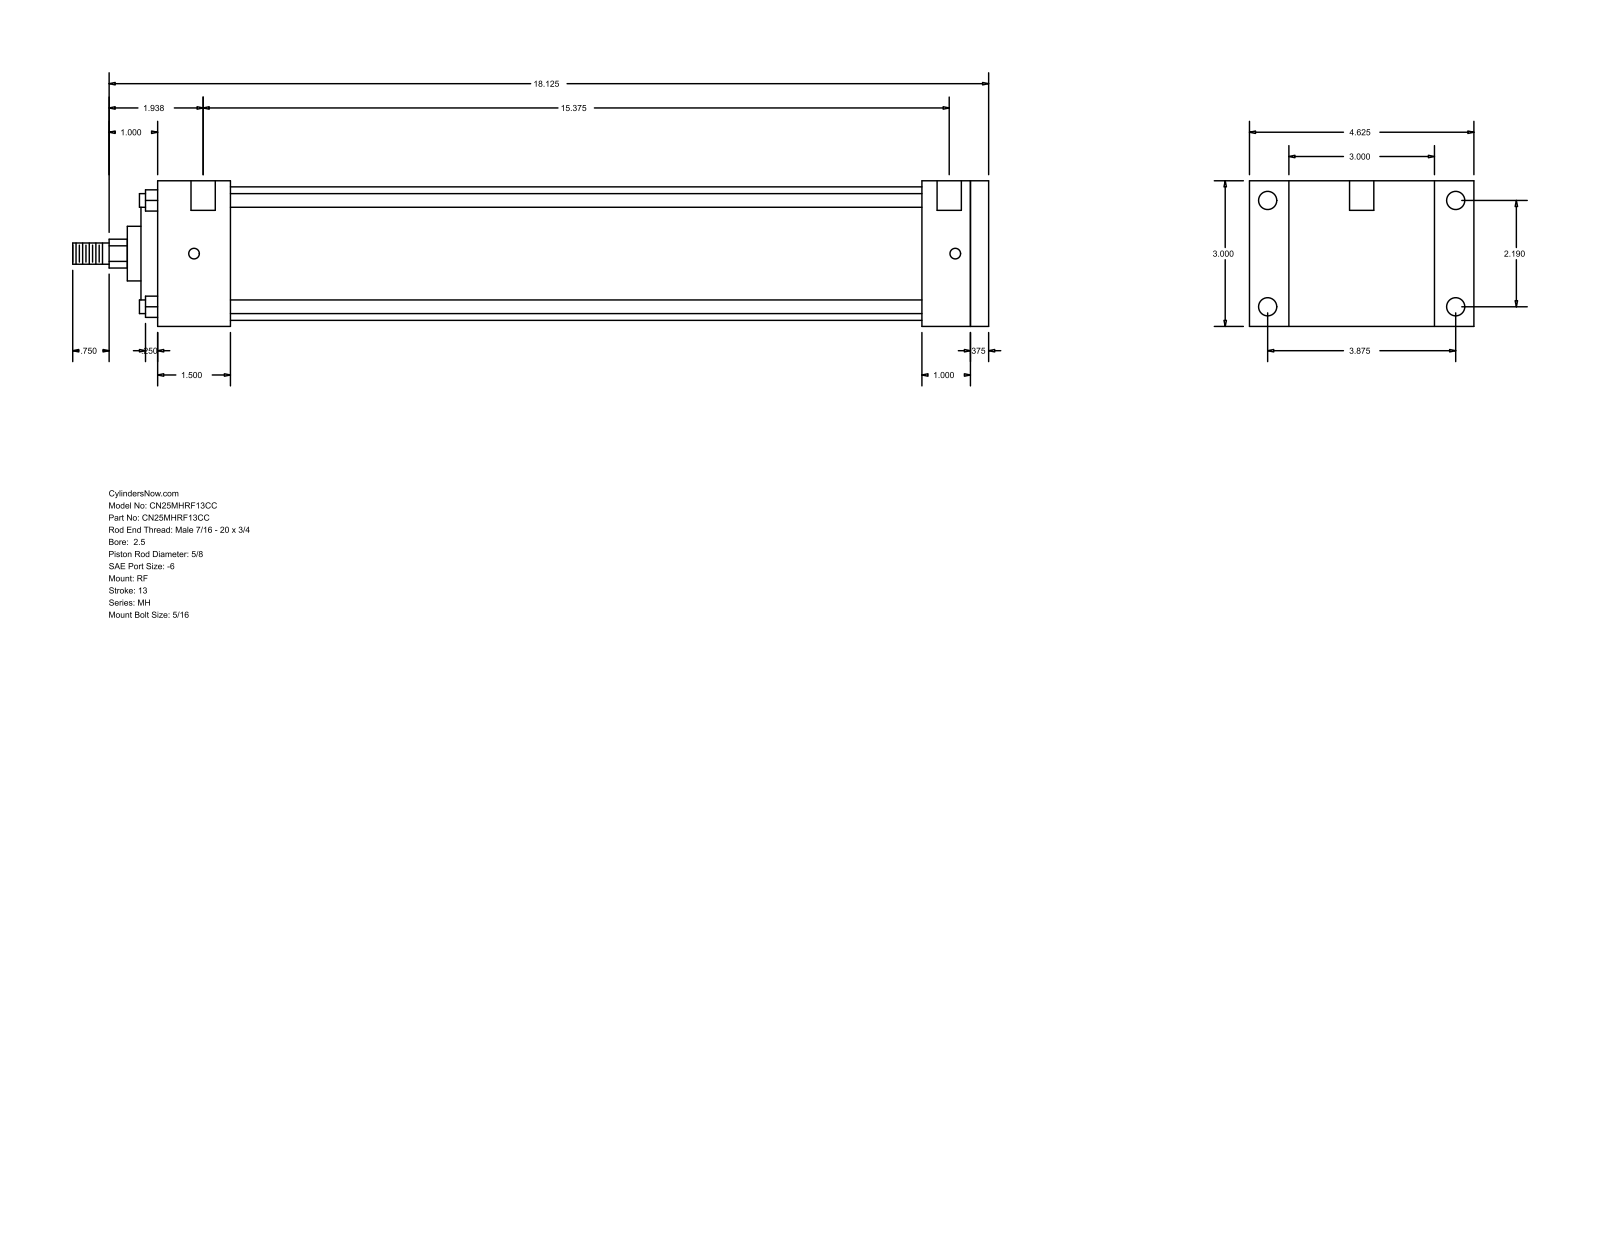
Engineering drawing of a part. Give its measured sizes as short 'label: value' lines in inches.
name: MH_RF__0250_0.625
written by: GSSL Pune (CONFIG_CONTROL_DESIGN)
unit: in
bodies: 0 solids, 94 faces (65 planar, 29 cylindrical, 0 other)
size: 18.875 × 4.625 × 3
holes: 4× ⌀0.219, 4× ⌀0.375, 2× ⌀0.5
bosses: 4× ⌀0.281, 1× ⌀2.75, 1× ⌀2.187, 1× ⌀1.125, 1× ⌀0.625, 1× ⌀0.437
rounds: 1× R0.297
face distances: 3, 0.375, 17.125, 16.75, 1, 1.375, 1.5, 15.75, 14.25, 15.25
hole spacings: 2.19, 3.875, 4.451, 15.687, 0.125, 0.187, 15.375, 15.5
